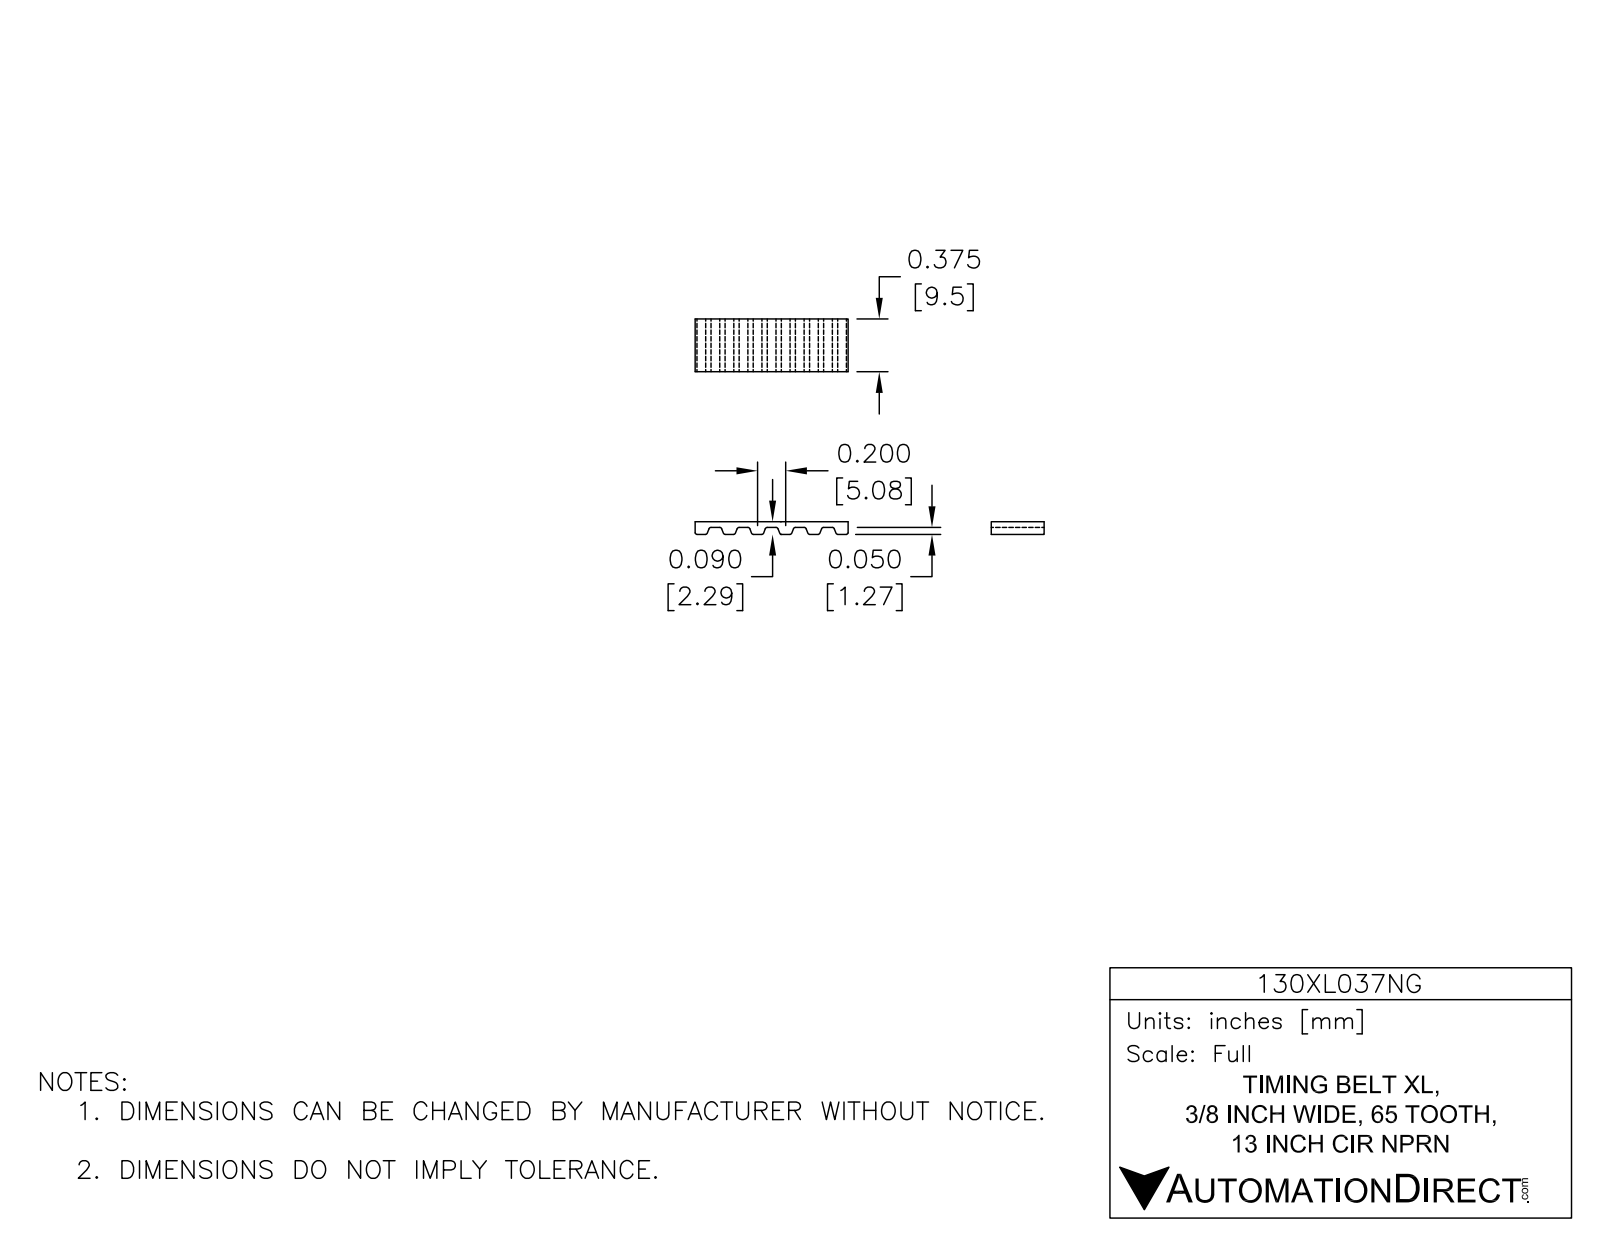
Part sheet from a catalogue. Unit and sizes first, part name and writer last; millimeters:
Units: millimetres
Overall size (bounding box): 121.6 × 76.2 × 9.5
Partial cylindrical surfaces — rounded edges, fillets, slot ends (radius × count): R0.4 ×260, R37.1 ×2, R38.1 ×2
Main face-to-face distances: 9.5, 76.2, 1, 75.2, 13.5, 74.2, 4.5, 9, 27.2, 27.1
Volume: 4 330 mm³ · Surface area: 8 006 mm²
Bodies: 1 solid, 558 faces (218 planar, 340 cylindrical, 0 other)
Part name (STEP PRODUCT): 130XL037NG
STEP written by: SolidWorks 2014 (AUTOMOTIVE_DESIGN)
